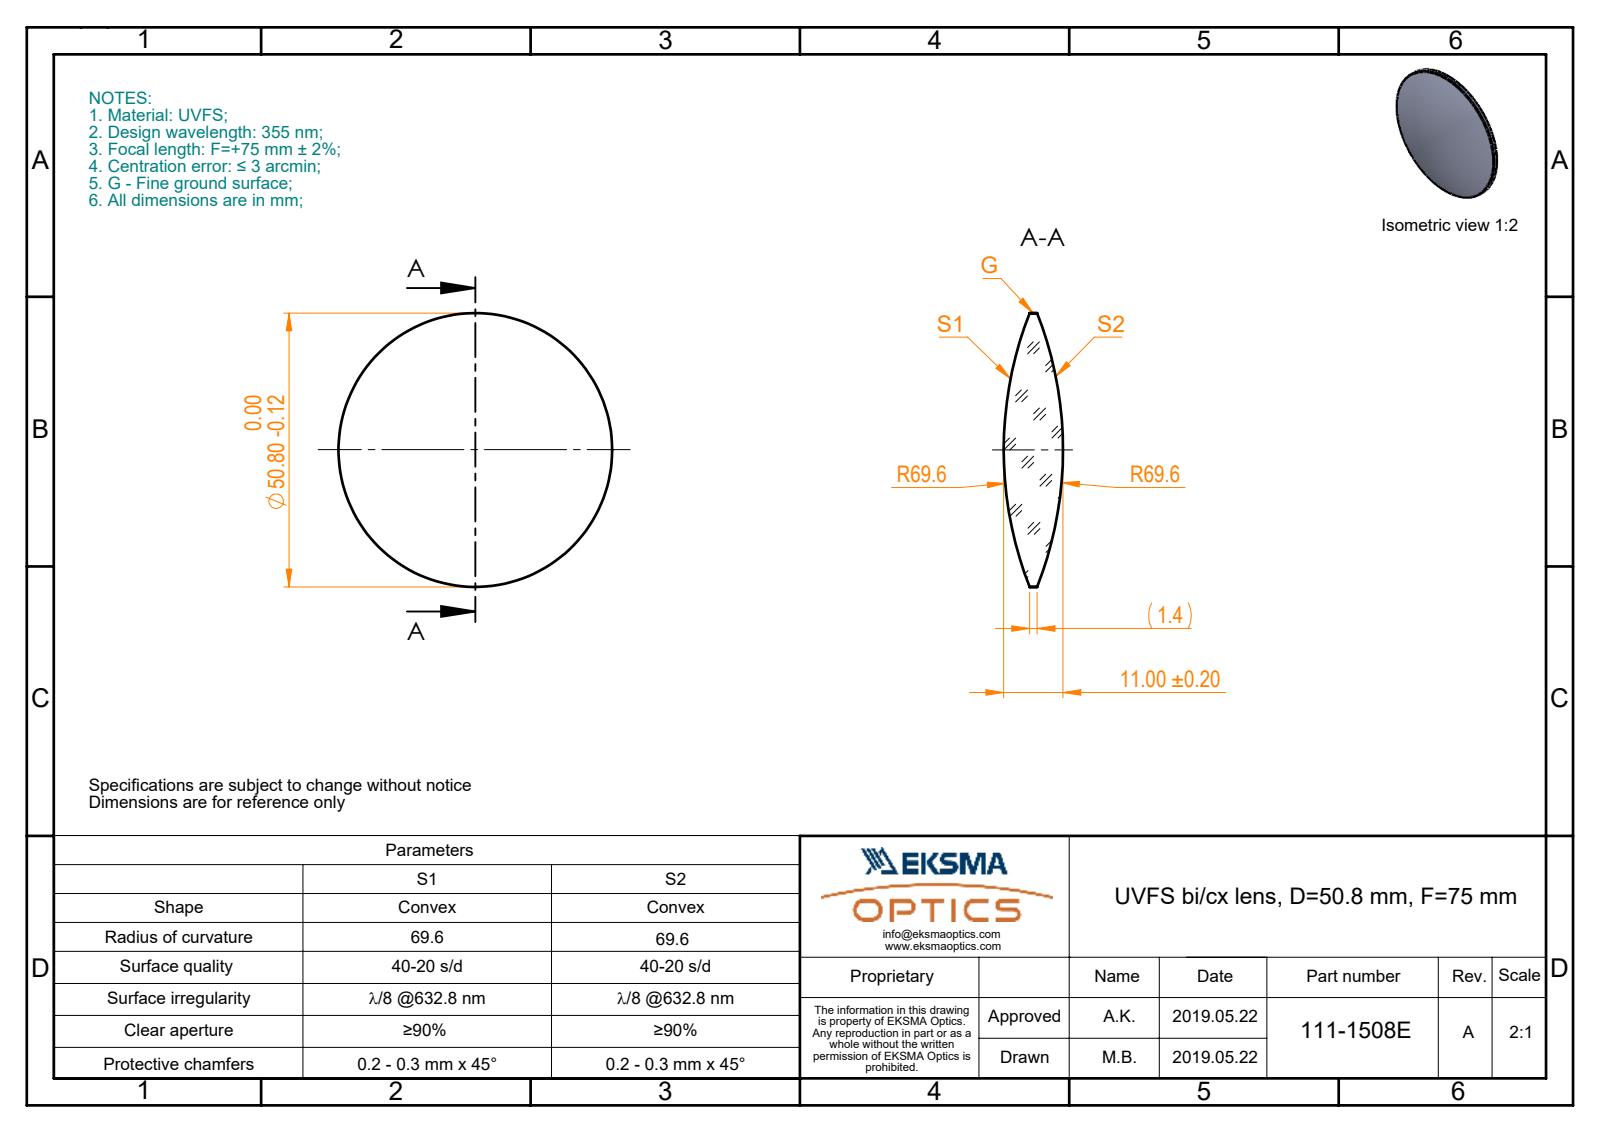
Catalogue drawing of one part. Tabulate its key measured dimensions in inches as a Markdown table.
| quantity | value |
| --- | --- |
| part name | 111-1508E UVFS bi-cx 50.8 F75 |
| STEP written by | SolidWorks 2017 (CONFIG_CONTROL_DESIGN) |
| units | inches |
| bodies | 1 solid, 6 faces (0 planar, 2 cylindrical, 4 other) |
| overall size | 2 × 2 × 0.433 |
| volume | 0.774 in³ |
| surface area | 6.854 in² |
| round bosses / shafts (diameter × count) | 2 × 1 |
